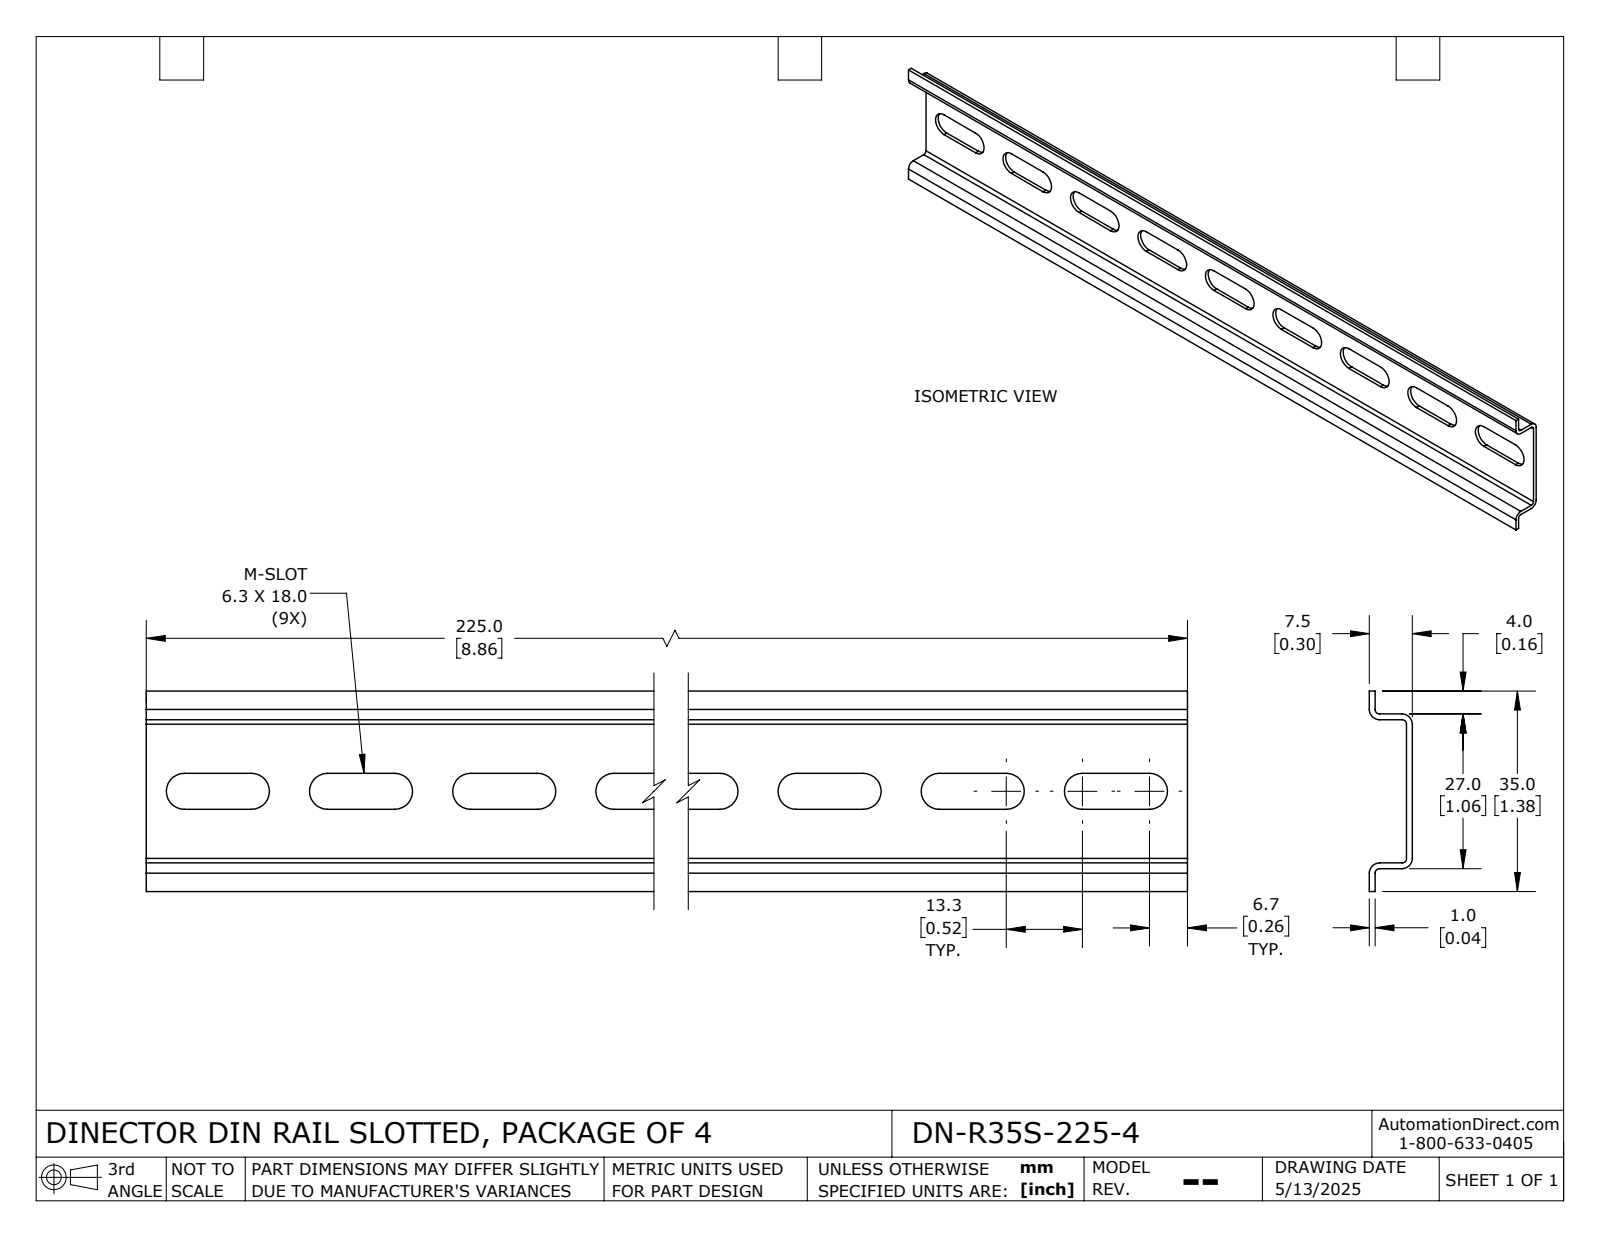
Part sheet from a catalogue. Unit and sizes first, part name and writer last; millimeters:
Units: millimetres
Overall size (bounding box): 225 × 35 × 7.5
Partial cylindrical surfaces — rounded edges, fillets, slot ends (radius × count): R3.15 ×18, R0.8 ×4, R1.8 ×4
Main face-to-face distances: 1, 6.5, 26, 7.5, 5.5, 27, 25, 4, 5, 30
Volume: 9 354 mm³ · Surface area: 19 638 mm²
Bodies: 1 solid, 58 faces (32 planar, 26 cylindrical, 0 other)
Part name (STEP PRODUCT): DN-R35S-225-4_Default
STEP written by: SolidWorks 2024 (CONFIG_CONTROL_DESIGN)
